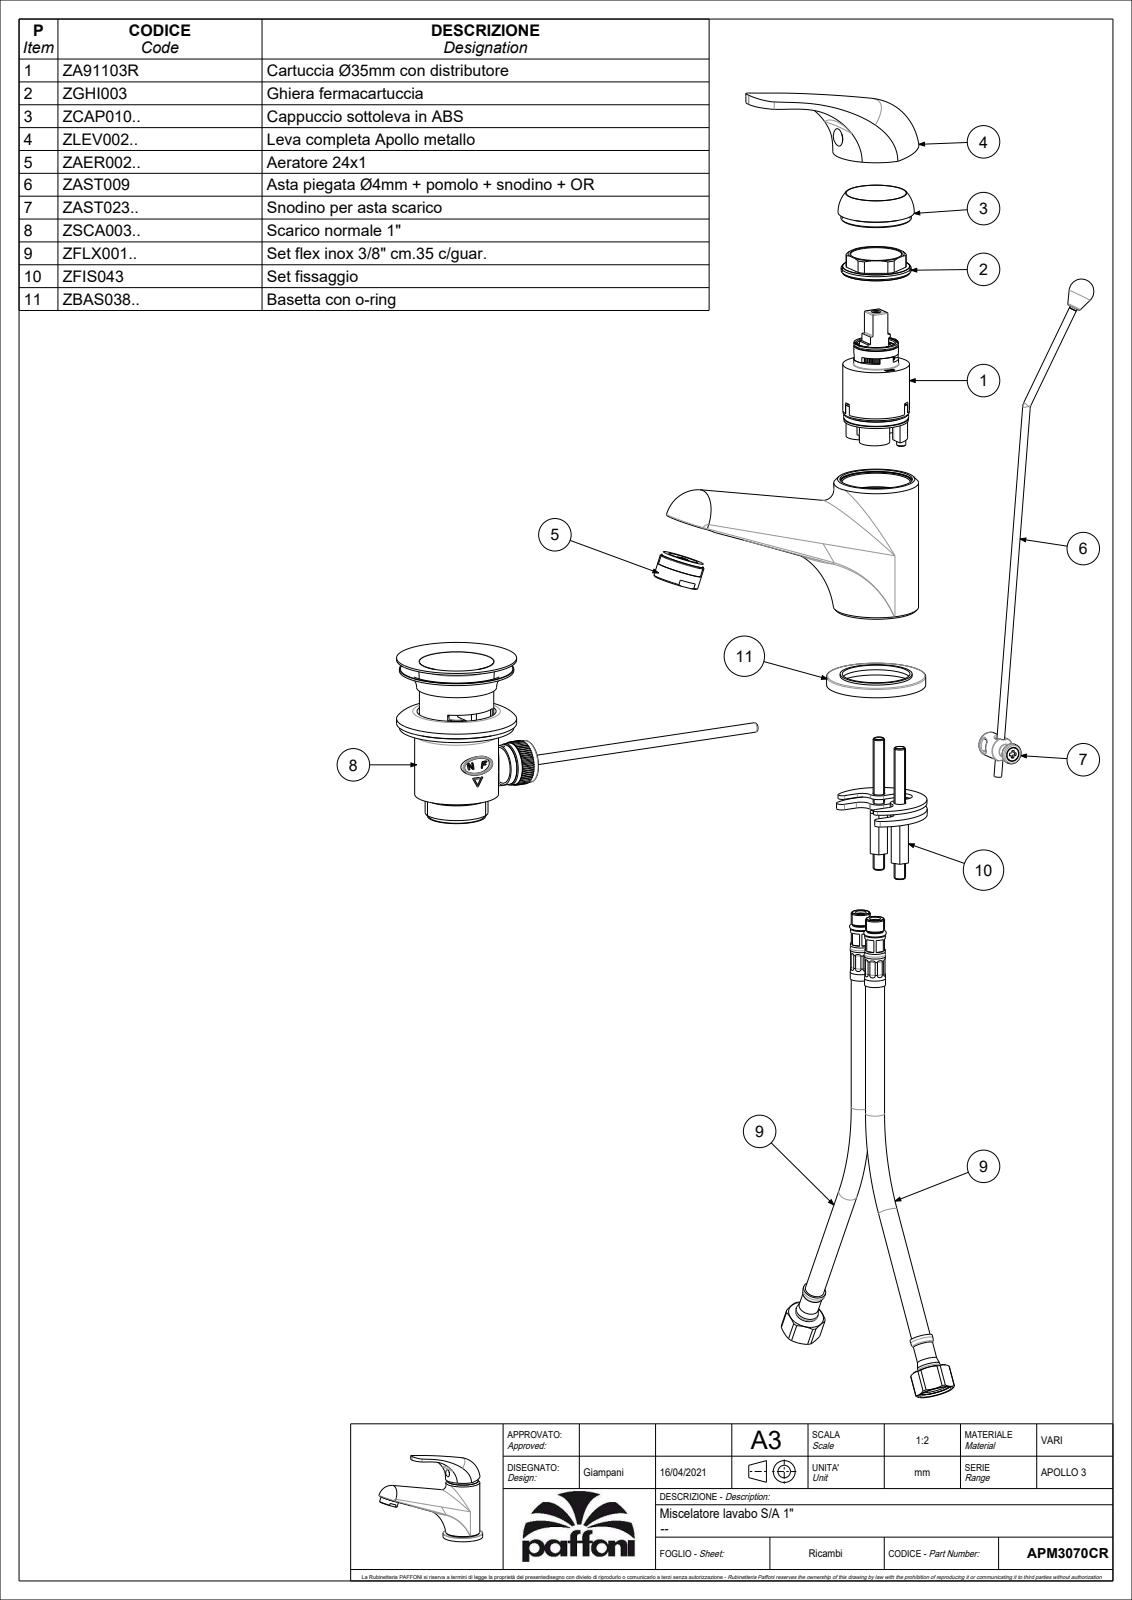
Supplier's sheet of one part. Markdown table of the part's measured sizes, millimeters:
| quantity | value |
| --- | --- |
| part name | APM3075CR |
| STEP written by | CREO PARAMETRIC BY PTC INC, 2020044 (CONFIG_CONTROL_DESIGN) |
| units | millimeters |
| bodies | 3 solids, 2759 faces (2034 planar, 348 cylindrical, 377 other) |
| overall size | 168.12 × 114.5 × 45.5 |
| volume | 121 771 mm³ |
| surface area | 83 657 mm² |
| round holes (diameter × count) | 9 × 5, 5 × 3, 12 × 3, 4 × 2, 7 × 2, 8 × 2, 11 × 2, 3.3 × 1, 4.5 × 1, 6 × 1, 16 × 1, 17 × 1 |
| round bosses / shafts (diameter × count) | 8 × 3, 44.5 × 1, 35 × 1, 34.8 × 1, 33.8 × 1, 32.2 × 1, 31.5 × 1, 29.8 × 1 |
| partial cylindrical surfaces (radius × count) | 0.5 × 43, 1 × 25, 0.15 × 11, 0.3 × 9, 1.5 × 8, 7 × 4, 4 × 2, 4.5 × 2 |
| main face-to-face distances | 0.5, 2.5, 3, 3.5, 2, 11.5, 4, 1, 1.5, 9.5 |
| hole center spacings | 13.6, 0.5, 0.71, 1.12, 8.51, 8.6, 9.01, 11.18 |
